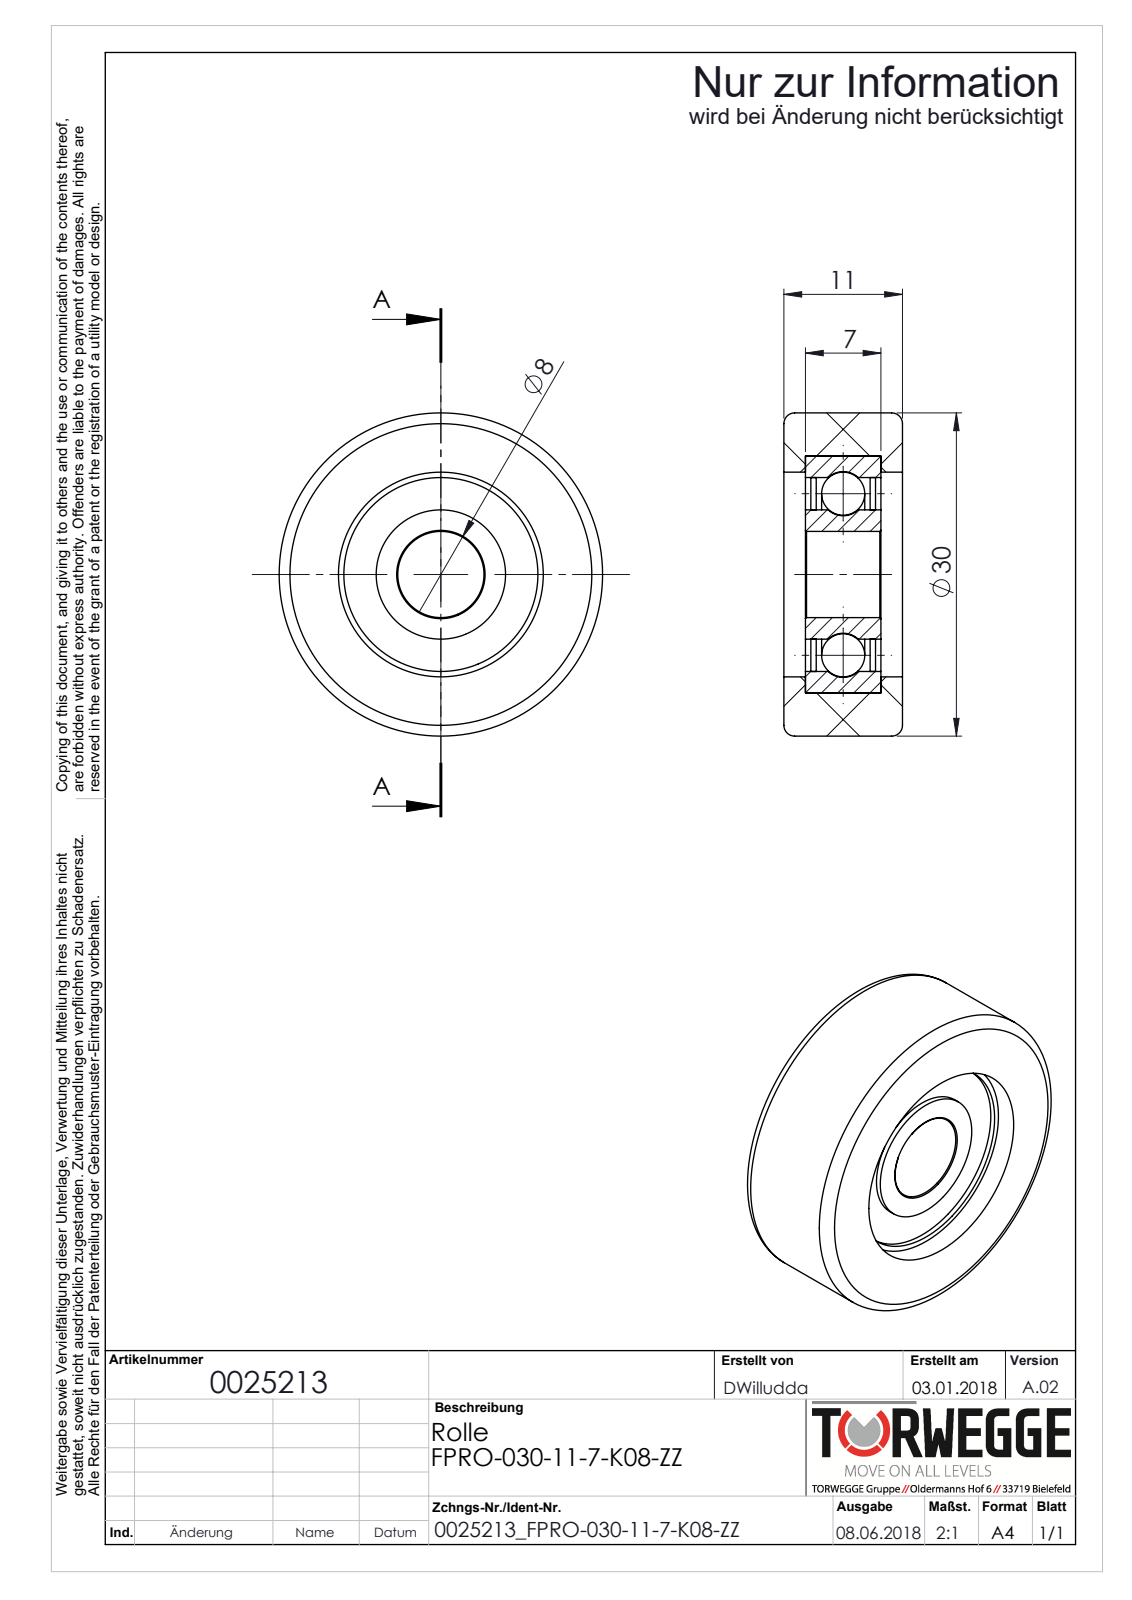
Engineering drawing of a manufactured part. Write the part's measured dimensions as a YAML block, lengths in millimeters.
part_name: "0025213_FPRO-030-11-7-K08-ZZ"
step_written_by: "SolidWorks 2018 (AUTOMOTIVE_DESIGN)"
units: millimeters
bodies: {solids: 0, faces: 32, planar: 8, cylindrical: 16, other: 8}
overall_size: [30, 30, 11]
round_holes:
  - {diameter: 8, count: 1}
  - {diameter: 18, count: 1}
  - {diameter: 19, count: 1}
round_bosses_or_shafts:
  - {diameter: 30, count: 1}
  - {diameter: 12, count: 1}
face_to_face_distances: [2, 9, 11, 2.5, 8.5, 0.5, 6.5, 7, 6]
